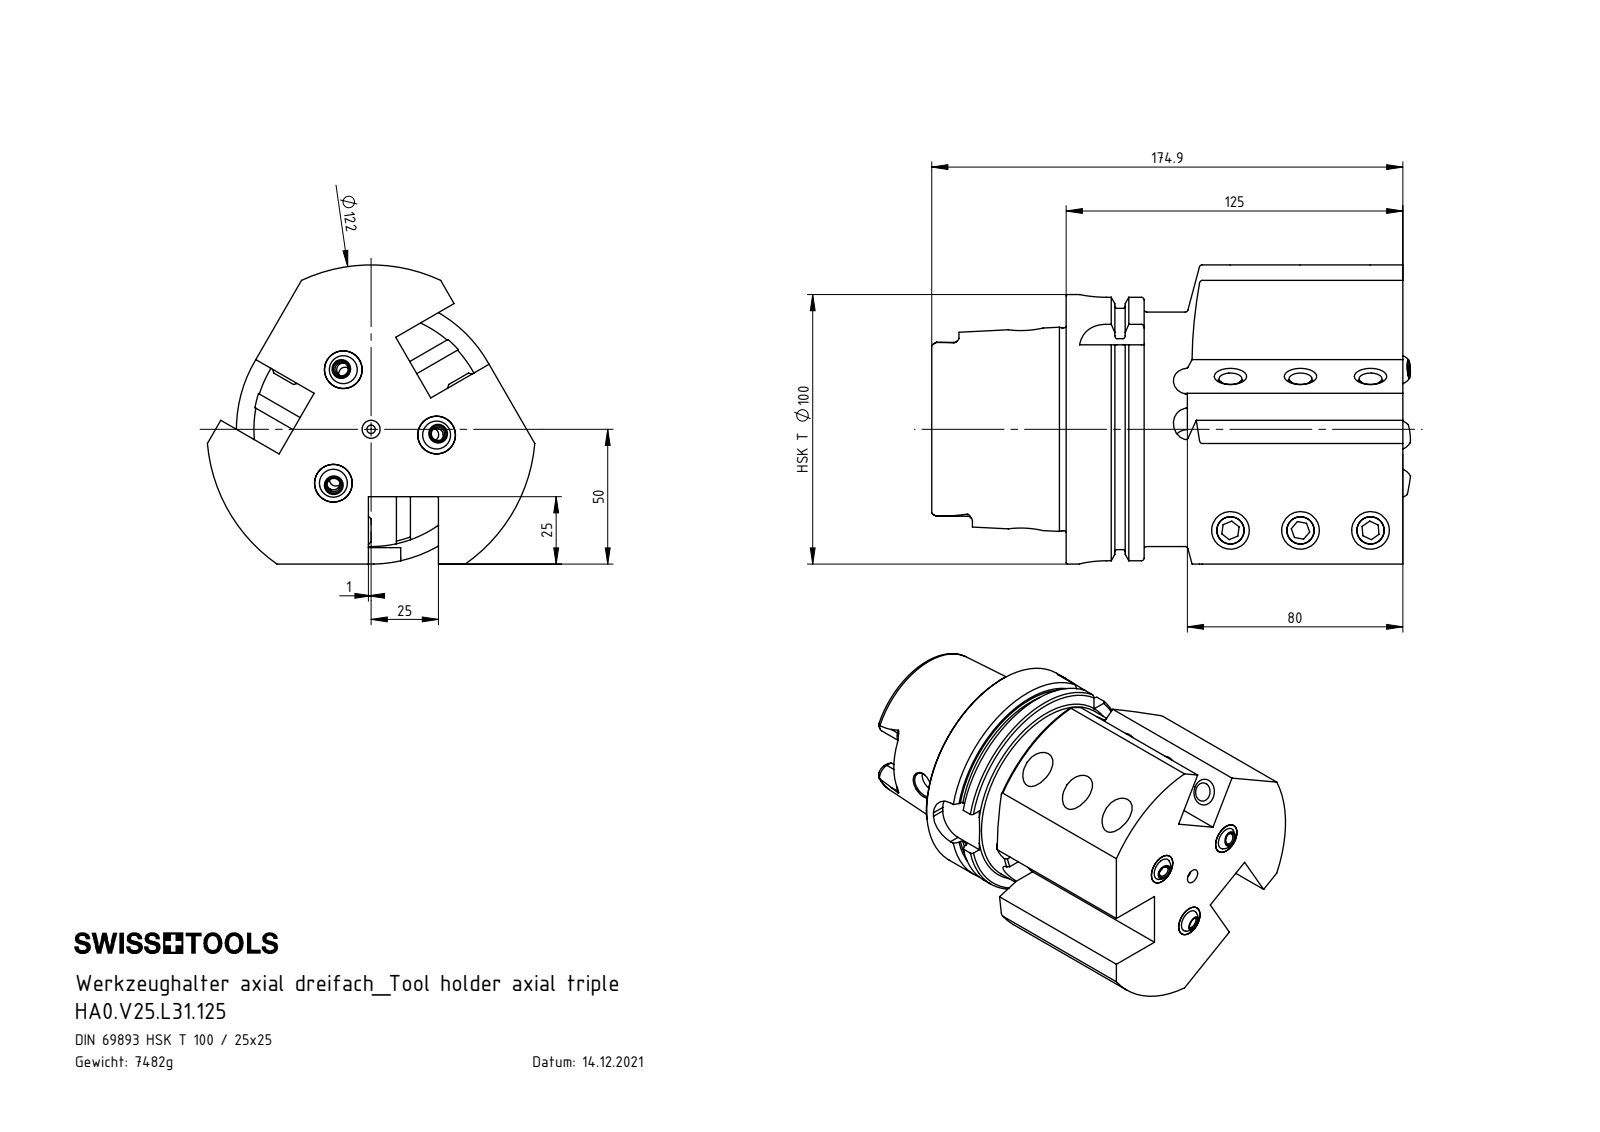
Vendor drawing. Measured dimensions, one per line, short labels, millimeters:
name: HA0.V25.L31.125; ISO 4026 - M12 x 25; KU1-U14.001.012; HA0-V25.L31.125_A_Fertigbearbeitung (+2 more)
written by: SolidWorks 2017 (AUTOMOTIVE_DESIGN)
unit: mm
bodies: 16 solids, 338 faces (149 planar, 84 cylindrical, 105 other)
size: 177.71 × 121.55 × 111
volume: 954 611 mm³; area: 135 892 mm²
holes: 12× ⌀14, 9× ⌀10.2, 6× ⌀5, 4× ⌀10, 2× ⌀12, 1× ⌀3.15, 1× ⌀22.5, 1× ⌀26, 1× ⌀53, 1× ⌀63
bosses: 9× ⌀12, 1× ⌀100, 1× ⌀91.95, 1× ⌀87, 1× ⌀75.26
rounds: 6× R1.9, 6× R5.2, 4× R4.88, 4× R10, 1× R61
face distances: 25, 26, 125, 12.45, 112.55, 28.95, 16.5, 96.05, 49.9, 62.35
hole spacings: 26, 24.41, 52, 42.28, 42.29, 65.74, 88.35, 112.44
